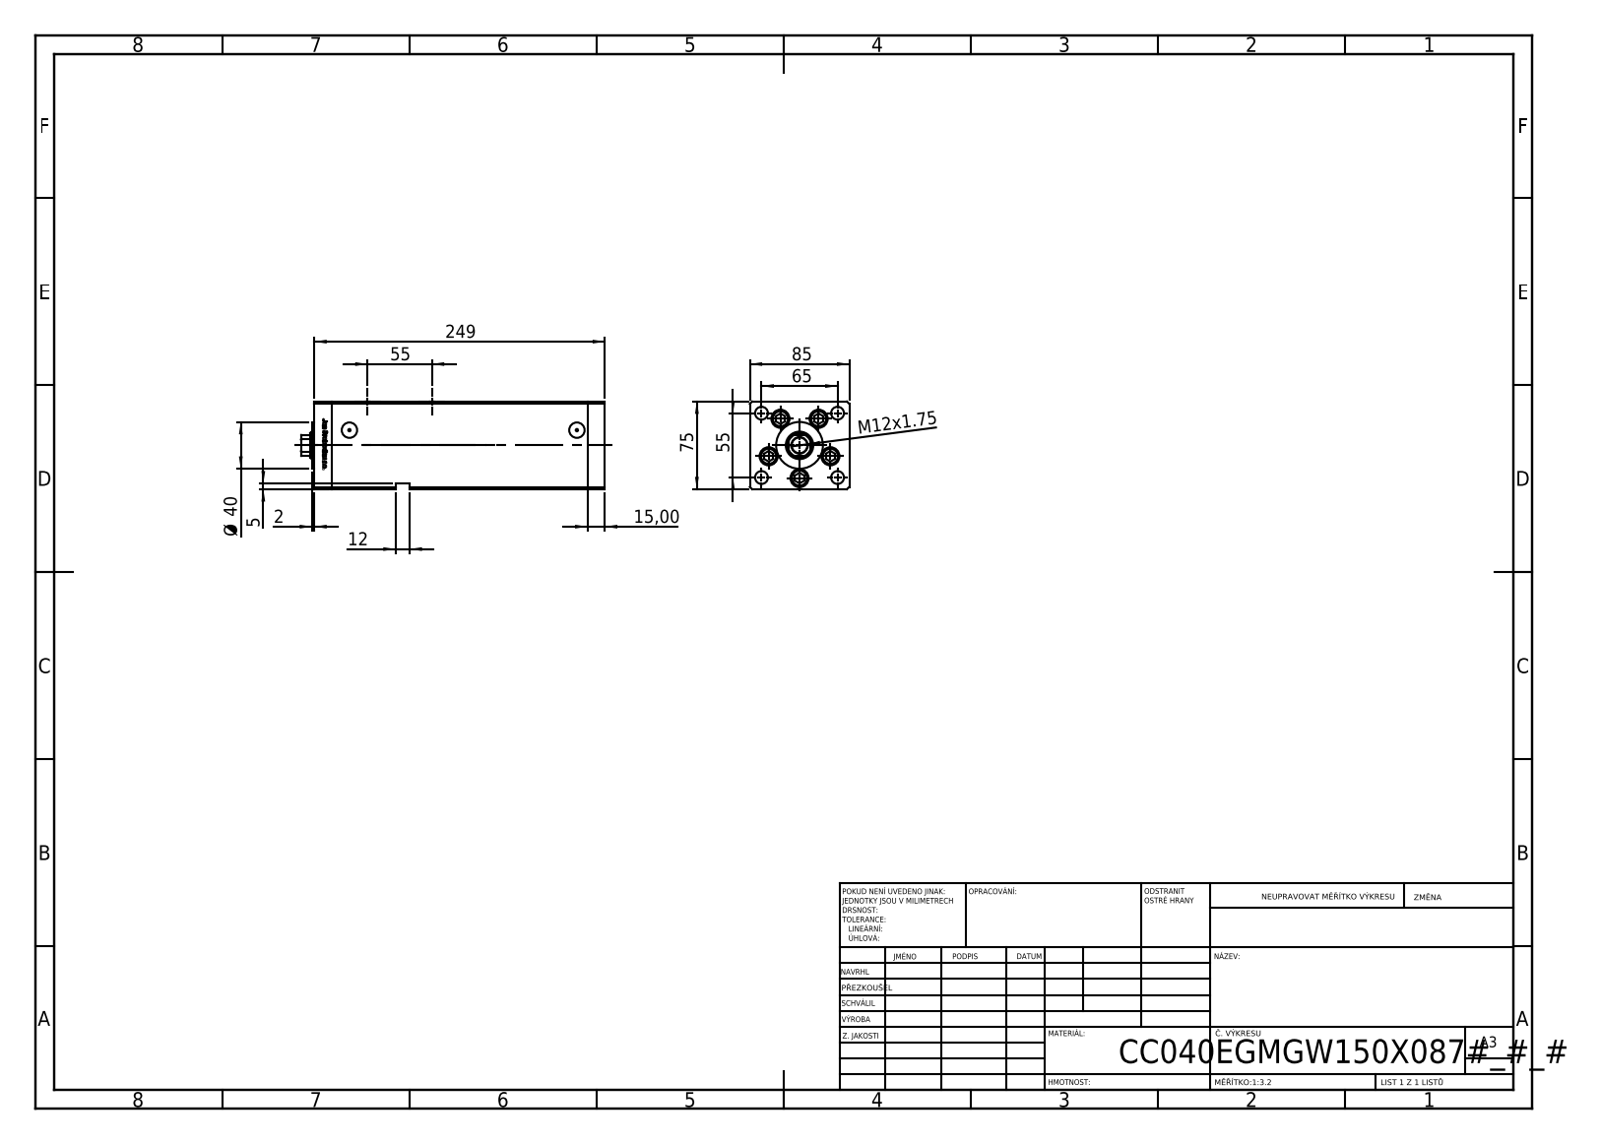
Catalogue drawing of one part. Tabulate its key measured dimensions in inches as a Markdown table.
| quantity | value |
| --- | --- |
| part name | V220C_VC_E; V220C BACK_E; ALLEN BOLT; V220C_FRONT_E (+1 more) |
| STEP written by | SolidWorks 2019 (CONFIG_CONTROL_DESIGN) |
| units | inches |
| bodies | 14 solids, 1214 faces (475 planar, 165 cylindrical, 574 other) |
| overall size | 10.236 × 3.346 × 2.953 |
| volume | 81.83 in³ |
| surface area | 324.8 in² |
| round holes (diameter × count) | 0.433 × 9, 0.61 × 5, 0.413 × 4, 0.65 × 4, 0.079 × 2, 0.518 × 2, 0.531 × 1, 0.866 × 1, 0.925 × 1 |
| round bosses / shafts (diameter × count) | 0.571 × 5, 0.315 × 5, 1.575 × 1 |
| partial cylindrical surfaces (radius × count) | 0.037 × 2, 0.413 × 1 |
| main face-to-face distances | 3.346, 2.953, 0.591, 8.602, 9.193, 9.783, 2.697, 0.413, 1.348, 2.539 |
| hole center spacings | 1.102, 1.676, 2.165, 2.559, 3.352, 0.664, 0.755, 1.273 |
